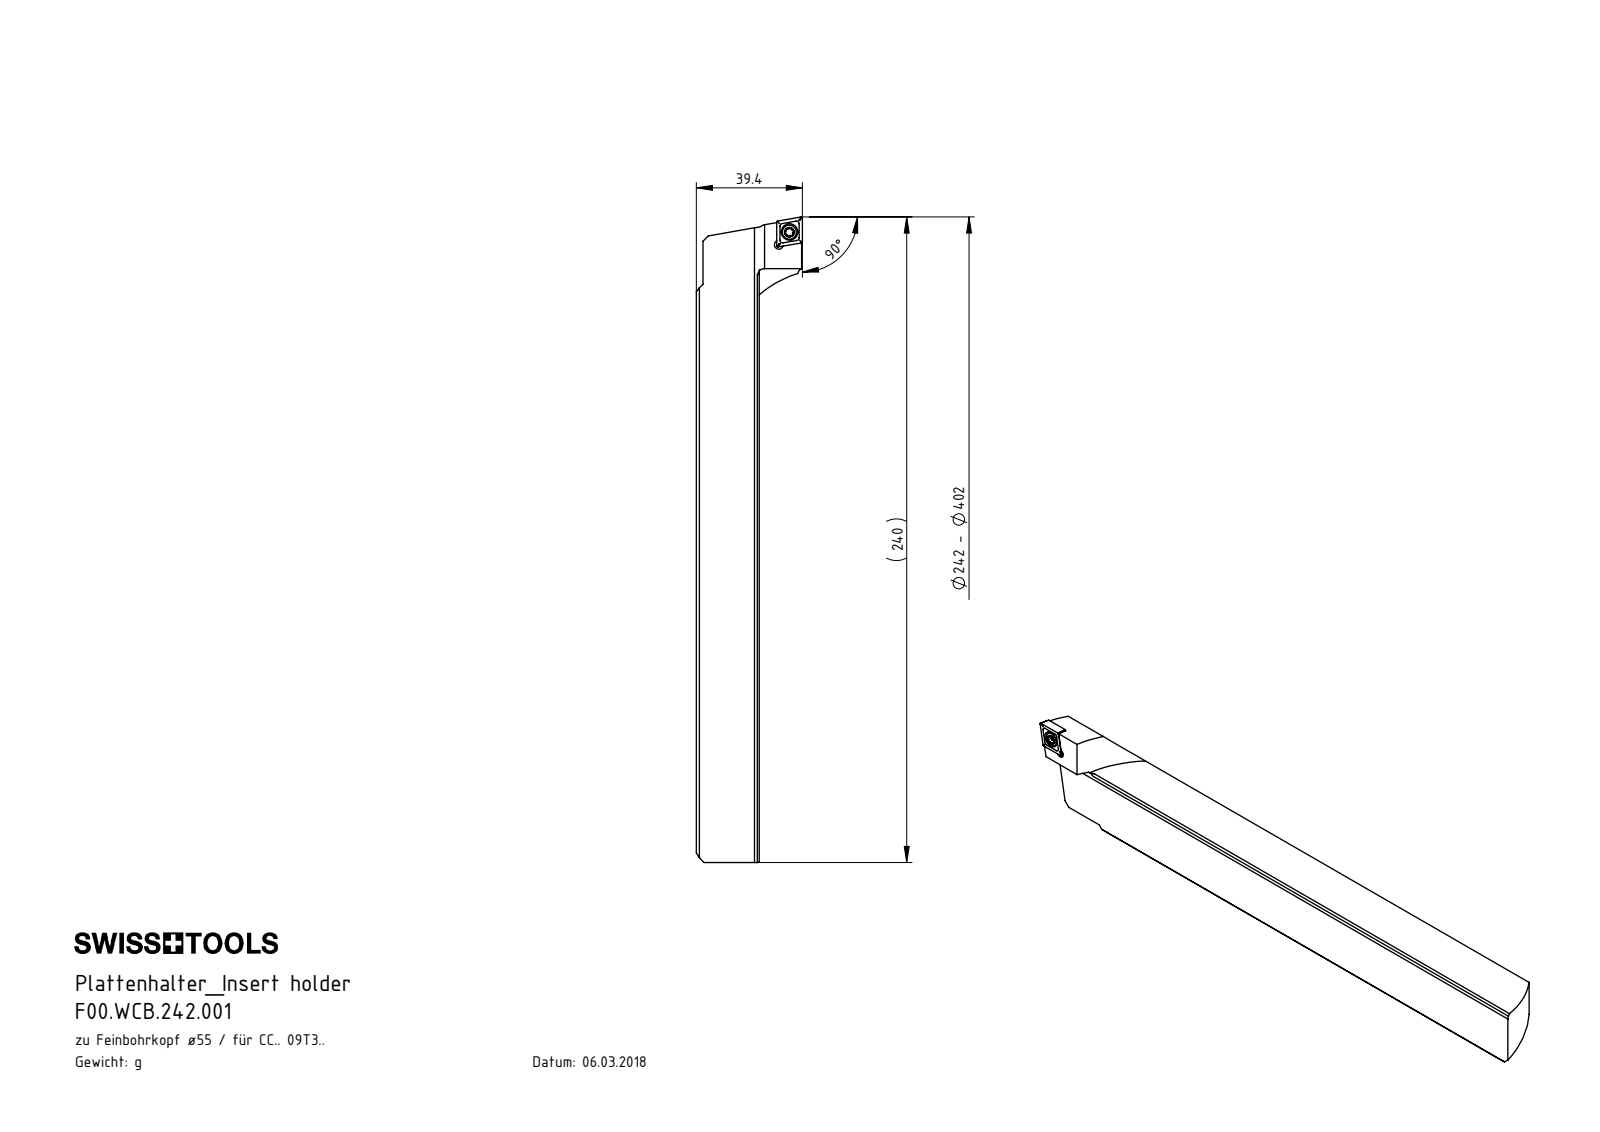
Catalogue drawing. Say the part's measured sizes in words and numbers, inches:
The part is named "CCMT09T304; WCB-ER2.001.009_A; F00.WCB.242.001; F00-WCB.242.001_C". Its 3-D file was written by "SolidWorks 2017 (AUTOMOTIVE_DESIGN)". It is 3 solids with 916 faces: 564 planar, 39 cylindrical and 313 other. Overall it measures 9.432 by 1.551 by 1.077 inches. Its volume is 6.119 cubic inches and its surface area 37.42 square inches. Round holes: 2 of diameter 0.13, 1 of diameter 0.173, 1 of diameter 0.24. Round bosses or shafts: 1 of diameter 0.207, 1 of diameter 0.157. Partial cylindrical surfaces (rounded edges, fillets, slot ends): 8 of radius 0.008, 6 of radius 0.013, 6 of radius 0.023, 3 of radius 1.575, 1 of radius 0.031. The main face-to-face distances are 0.094, 0.187, 0.839, 0.281, 0.375, 0.188, 0.281, 0.375, 0.469, 0.563. The hole center spacings are 0.239, 0.244.
